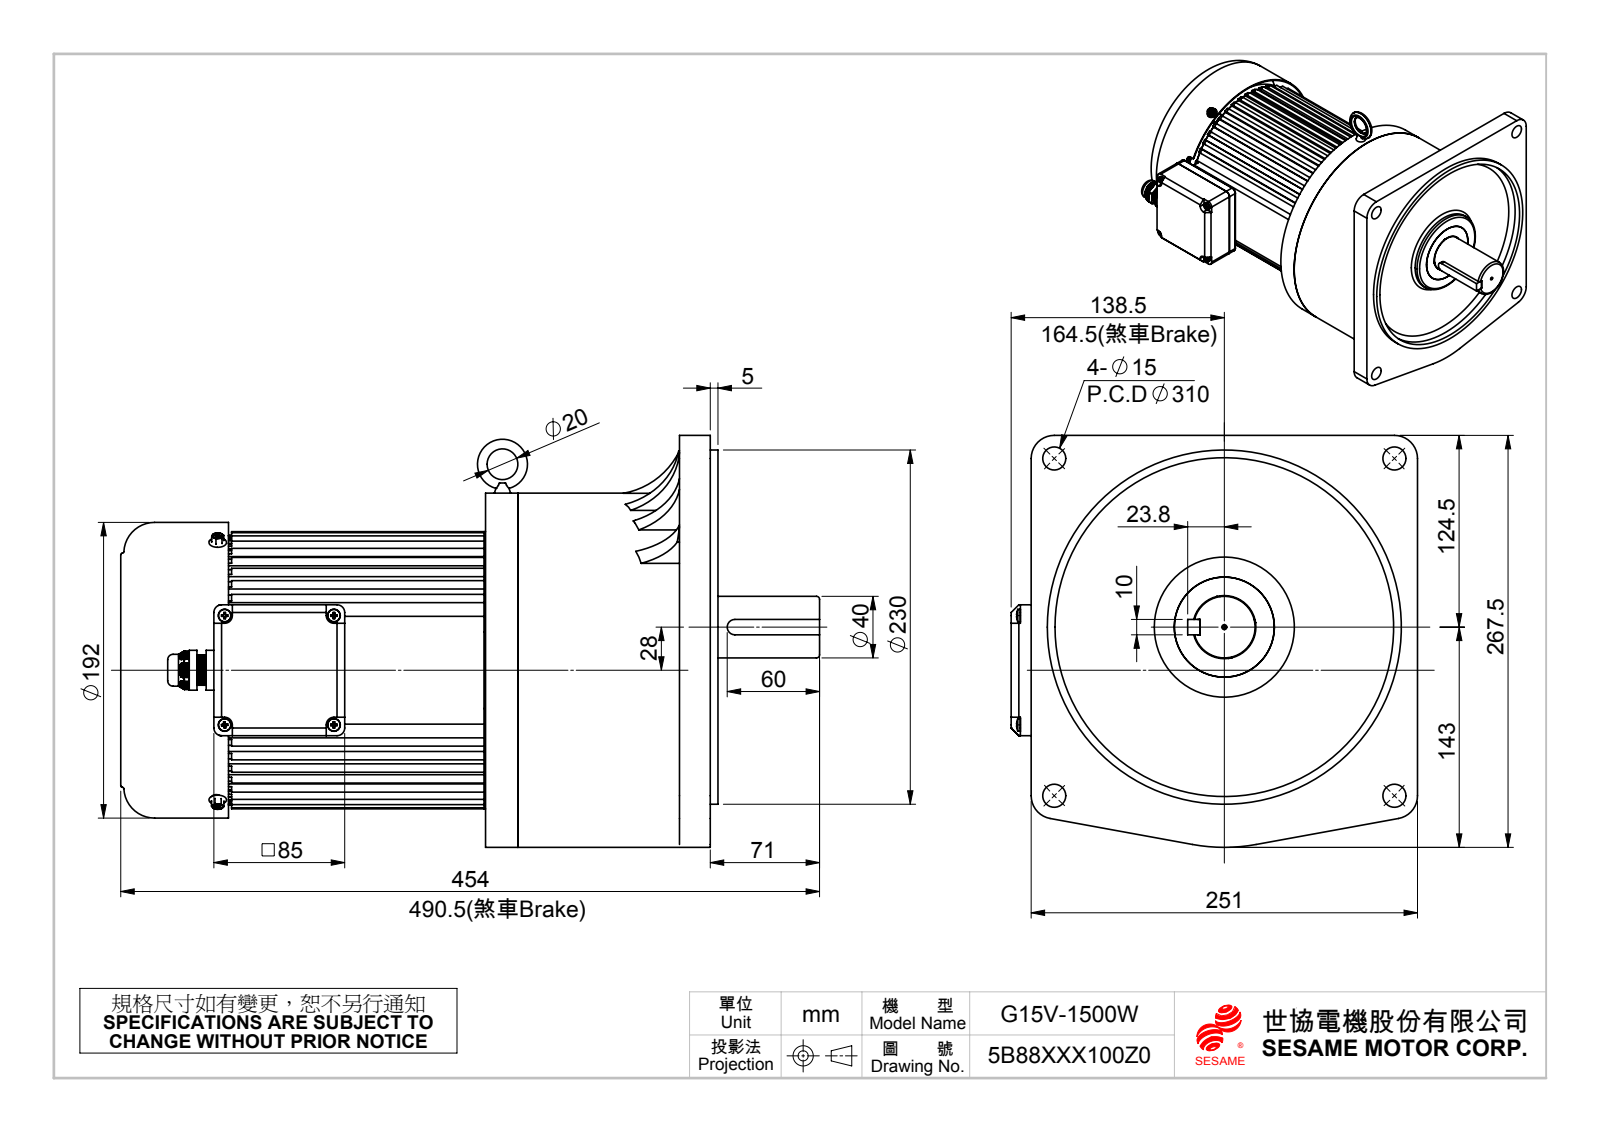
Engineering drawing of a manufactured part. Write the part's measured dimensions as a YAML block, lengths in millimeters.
part_name: "出線盒下蓋; 外六角內十字螺絲M5 x 10_ISO 4162 - M5 x 10 x 10-N; 10x8xL_60L; M8x16吊環(G14.G15前蓋用) (+8 more)"
step_written_by: "SolidWorks 2010 (CONFIG_CONTROL_DESIGN)"
units: millimeters
bodies: {solids: 20, faces: 3144, planar: 1208, cylindrical: 877, other: 1059}
overall_size: [454, 267.5, 264]
volume: 11220000
surface_area: 826329
round_holes:
  - {diameter: 5, count: 11}
  - {diameter: 3.3, count: 9}
  - {diameter: 6, count: 4}
  - {diameter: 8, count: 4}
  - {diameter: 15, count: 4}
  - {diameter: 4.2, count: 3}
  - {diameter: 2, count: 1}
  - {diameter: 6.5, count: 1}
  - {diameter: 6.8, count: 1}
  - {diameter: 10.8, count: 1}
  - {diameter: 16.5, count: 1}
  - {diameter: 20, count: 1}
round_bosses_or_shafts:
  - {diameter: 8.3, count: 4}
  - {diameter: 4, count: 4}
  - {diameter: 5, count: 3}
  - {diameter: 230, count: 2}
  - {diameter: 192, count: 1}
  - {diameter: 190, count: 1}
  - {diameter: 180, count: 1}
  - {diameter: 171, count: 1}
partial_cylinders:
  - {radius: 2.25, count: 42}
  - {radius: 0.5, count: 24}
  - {radius: 1, count: 24}
  - {radius: 5, count: 15}
  - {radius: 50, count: 7}
  - {radius: 2.9, count: 6}
  - {radius: 15, count: 6}
  - {radius: 2, count: 4}
face_to_face_distances: [195, 5, 27, 1, 168, 147, 113, 308, 140, 236]
hole_center_spacings: [45, 58.25, 71, 82.38, 11, 11.5, 14.6, 14.79]
